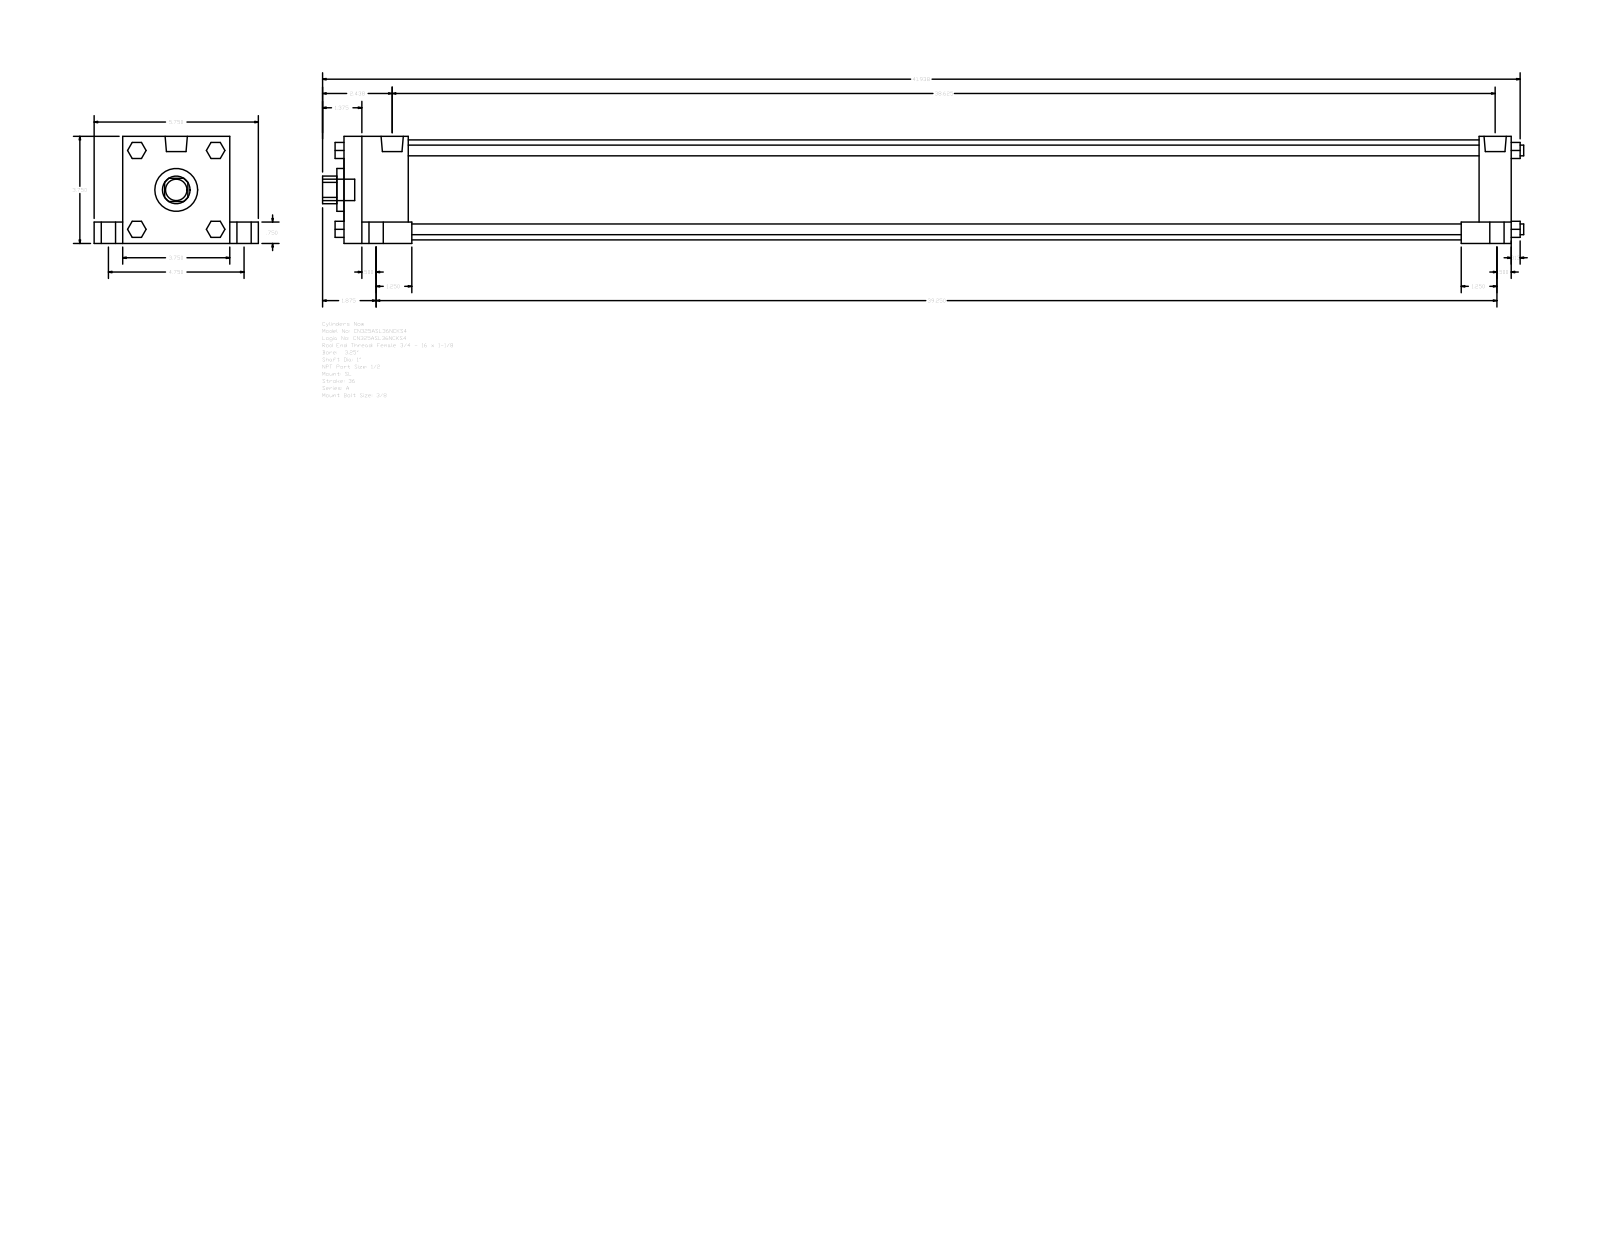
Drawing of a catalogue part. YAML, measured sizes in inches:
part_name: "A_SL__0325_1"
step_written_by: "GSSL Pune (CONFIG_CONTROL_DESIGN)"
units: inches
bodies: {solids: 0, faces: 150, planar: 114, cylindrical: 36, other: 0}
overall_size: [42.063, 5.75, 3.75]
round_holes:
  - {diameter: 1, count: 1}
  - {diameter: 1.5, count: 1}
  - {diameter: 3.5, count: 1}
round_bosses_or_shafts:
  - {diameter: 0.75, count: 5}
  - {diameter: 0.5, count: 4}
  - {diameter: 0.375, count: 4}
  - {diameter: 0.344, count: 4}
  - {diameter: 0.778, count: 2}
partial_cylinders:
  - {radius: 0.484, count: 1}
face_to_face_distances: [3.75, 40.875, 0.75, 1, 4.75, 3, 0.625, 2.25, 39.75, 37.5]
